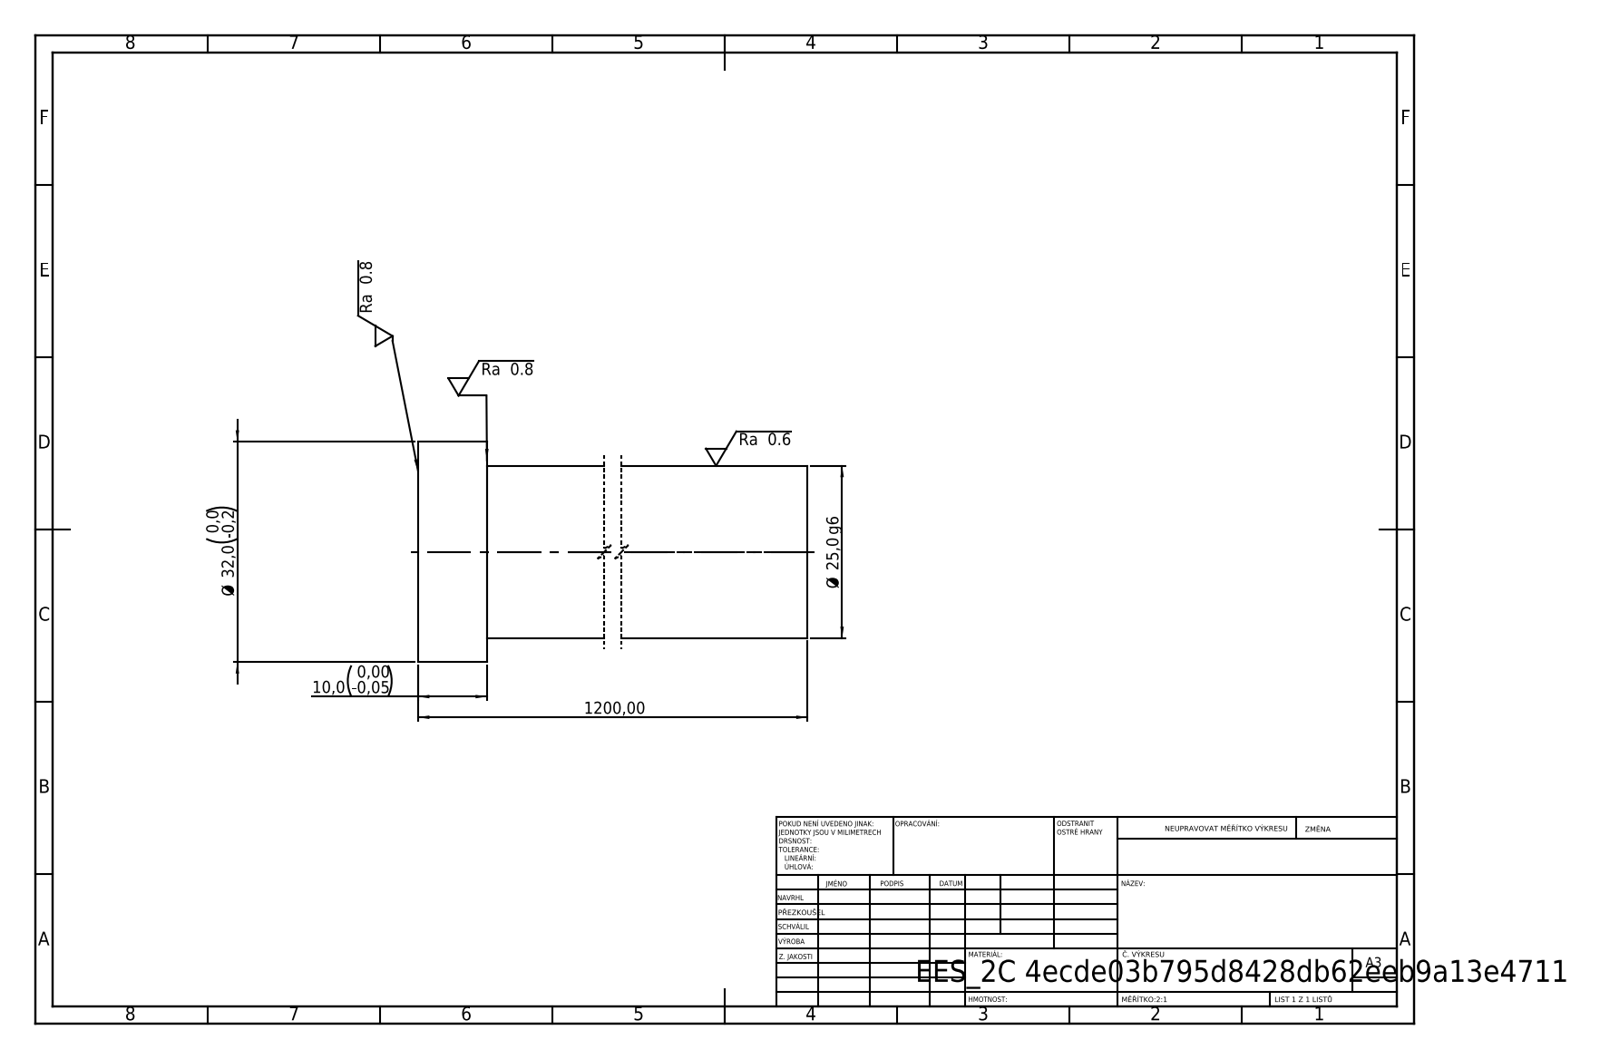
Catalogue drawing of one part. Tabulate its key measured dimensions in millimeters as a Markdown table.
| quantity | value |
| --- | --- |
| STEP written by | SolidWorks 2019 (CONFIG_CONTROL_DESIGN) |
| units | millimeters |
| bodies | 1 solid, 7 faces (3 planar, 4 cylindrical, 0 other) |
| overall size | 1200 × 32 × 32 |
| volume | 592 182 mm³ |
| surface area | 96 076 mm² |
| round bosses / shafts (diameter × count) | 32 × 1, 25 × 1 |
| main face-to-face distances | 1200, 10, 1190 |
